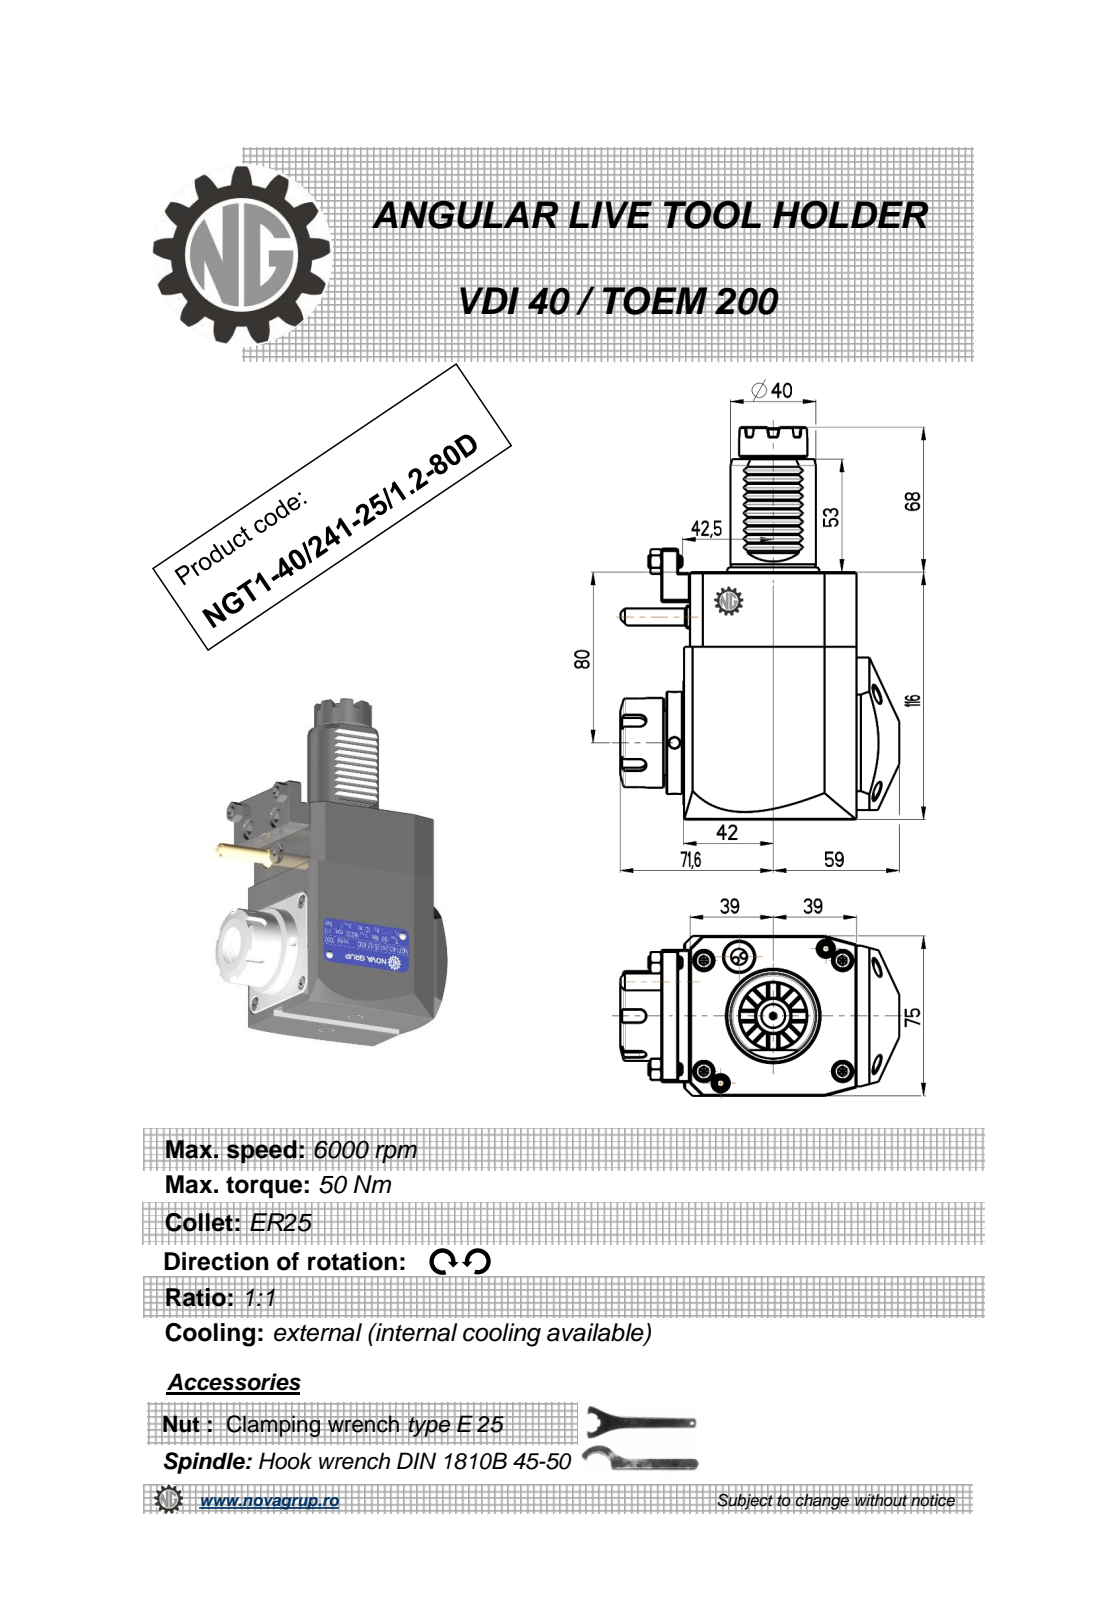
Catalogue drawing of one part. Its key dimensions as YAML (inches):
part_name: "NGT1_40_241_25_1_2_80D"
step_written_by: "PRO/ENGINEER BY PARAMETRIC TECHNOLOGY CORPORATION, 2010280 (CONFIG_CONTROL_DESIGN)"
units: inches
bodies: {solids: 1, faces: 496, planar: 208, cylindrical: 89, other: 199}
overall_size: [7.244, 5.142, 3.016]
volume: 53.05
surface_area: 110.6
round_holes:
  - {diameter: 0.197, count: 3}
  - {diameter: 0.118, count: 1}
  - {diameter: 0.799, count: 1}
round_bosses_or_shafts:
  - {diameter: 0.236, count: 2}
  - {diameter: 1.89, count: 1}
  - {diameter: 1.654, count: 1}
  - {diameter: 1.575, count: 1}
  - {diameter: 1.476, count: 1}
  - {diameter: 1.299, count: 1}
  - {diameter: 1.26, count: 1}
  - {diameter: 0.669, count: 1}
partial_cylinders:
  - {radius: 0.012, count: 10}
  - {radius: 0.012, count: 10}
  - {radius: 0.009, count: 6}
  - {radius: 0.118, count: 5}
  - {radius: 0.02, count: 1}
  - {radius: 0.339, count: 1}
  - {radius: 1.575, count: 1}
face_to_face_distances: [2.953, 4.567, 3.189, 0.531, 0.02, 3.181, 0.433, 0.315, 0.413, 0.098]
hole_center_spacings: [2.407]
